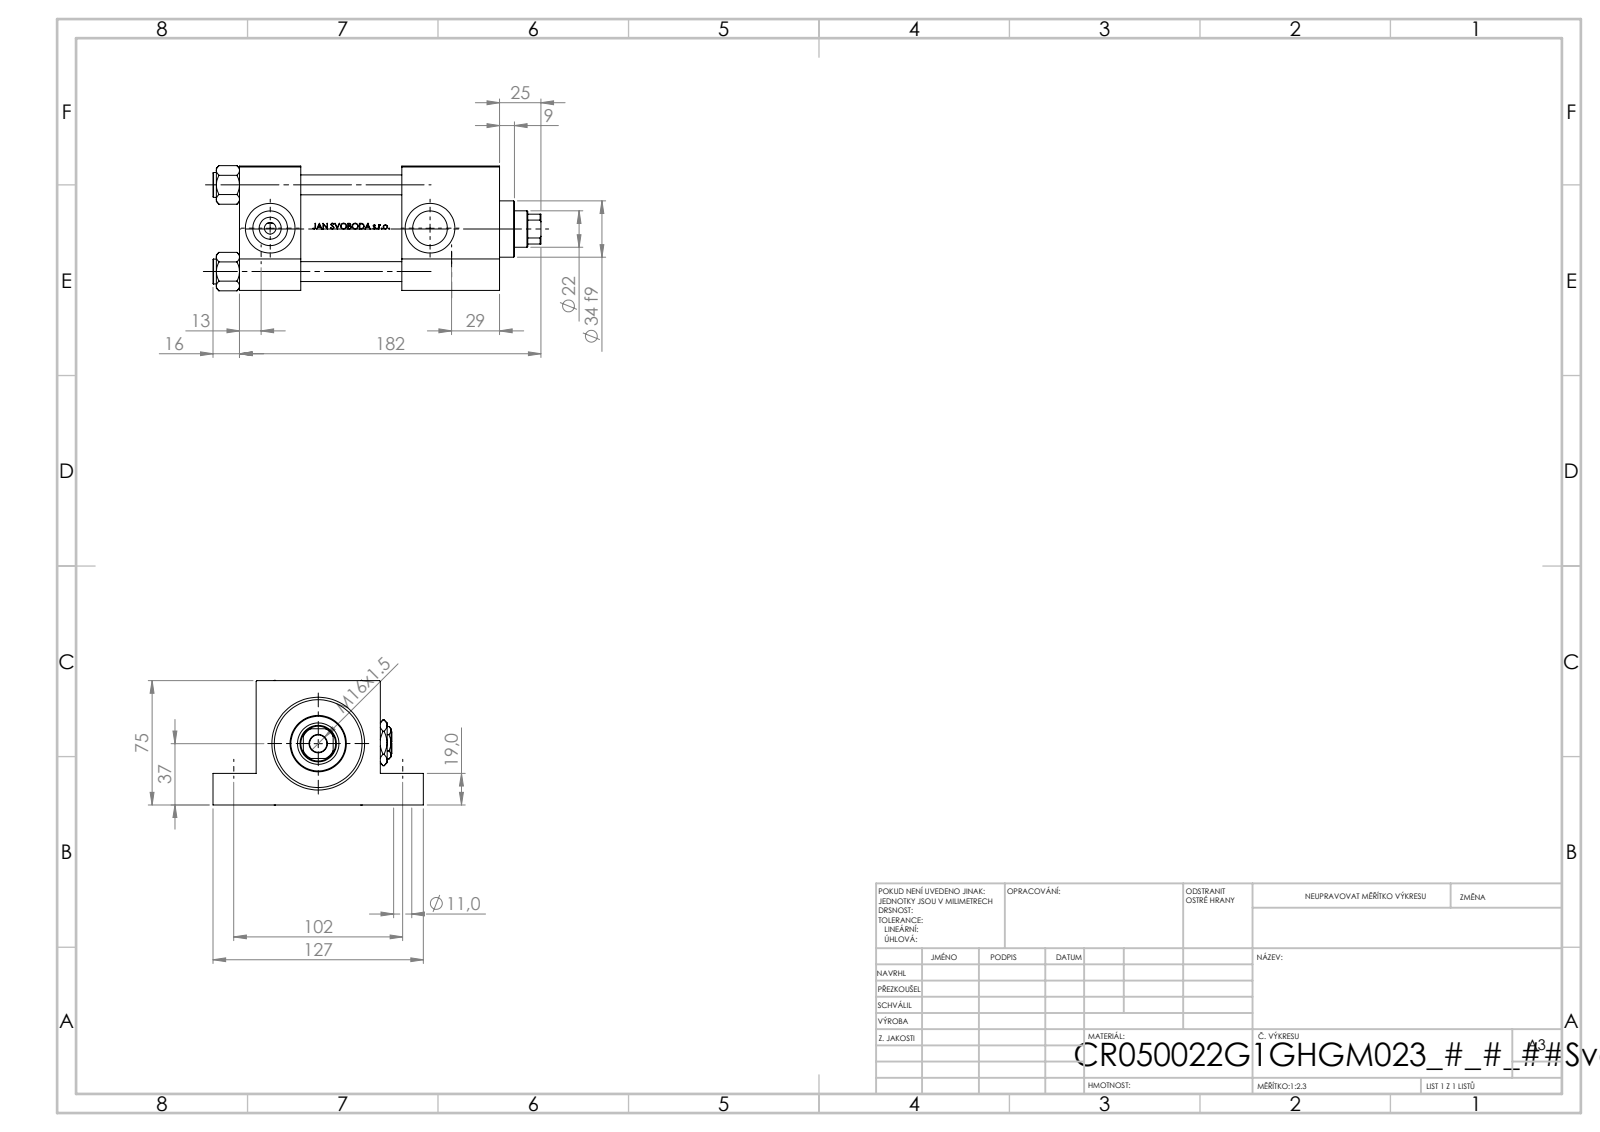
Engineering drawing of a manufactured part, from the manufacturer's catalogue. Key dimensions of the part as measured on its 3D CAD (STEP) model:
Part name (STEP PRODUCT): V215CR_G_Body; NUT_M5_G; Zatka_pro_OIL_PORT; V215_VC_A (+2 more)
STEP written by: SolidWorks 2019 (CONFIG_CONTROL_DESIGN)
Units: millimetres
Bodies: 12 solids, 1134 faces (454 planar, 128 cylindrical, 552 other)
Overall size (bounding box): 198 × 127 × 75.54
Volume: 756 399 mm³ · Surface area: 162 962 mm²
Round holes (diameter × count): ⌀11 ×4, ⌀12 ×4, ⌀7 ×2, ⌀20.96 ×2, ⌀30 ×2, ⌀10.5 ×1, ⌀22 ×1, ⌀25 ×1, ⌀41 ×1, ⌀50 ×1, ⌀53 ×1
Round bosses / shafts (diameter × count): ⌀15 ×4, ⌀56 ×1, ⌀34 ×1
Partial cylindrical surfaces — rounded edges, fillets, slot ends (radius × count): R10.5 ×1
Main face-to-face distances: 75, 37, 157, 120, 19, 56, 98, 61, 59, 26
Hole centre spacings: 52.3, 36.63, 37.34, 73.96, 102, 115, 153.72, 96.5
